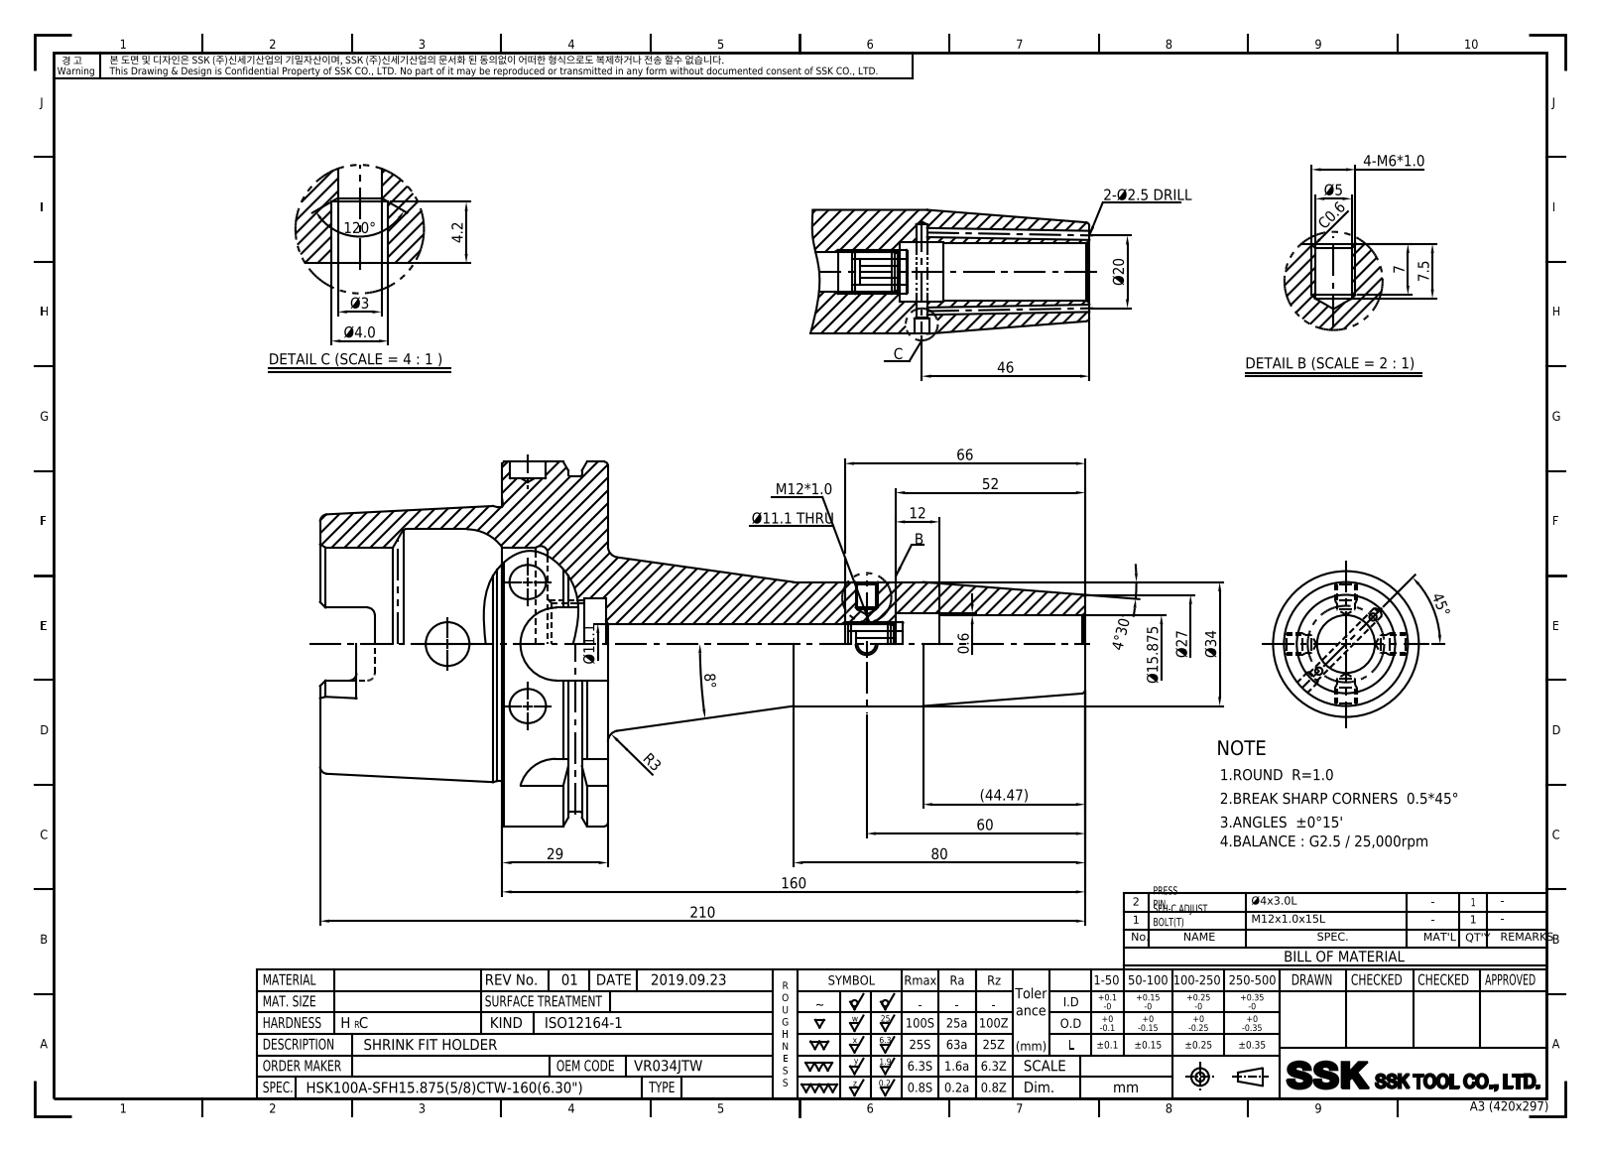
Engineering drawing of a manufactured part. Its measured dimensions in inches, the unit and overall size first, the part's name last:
Units: inches
Overall size (bounding box): 8.268 × 3.937 × 3.937
Round holes (diameter × count): ⌀0.079 ×2, ⌀0.394 ×1, ⌀0.43 ×1, ⌀0.472 ×1, ⌀0.625 ×1, ⌀0.672 ×1, ⌀0.881 ×1, ⌀0.984 ×1, ⌀2.087 ×1, ⌀2.48 ×1
Round bosses / shafts (diameter × count): ⌀3.937 ×1, ⌀3.622 ×1, ⌀2.969 ×1, ⌀1.339 ×1
Partial cylindrical surfaces — rounded edges, fillets, slot ends (radius × count): R0.079 ×6, R0.192 ×4, R0.394 ×4
Main face-to-face distances: 1.142, 0.492, 0.65, 3.11, 2.461, 1.969, 3.465, 3.091, 1.122, 0.63
Volume: 22.54 in³ · Surface area: 107.1 in²
Bodies: 1 solid, 118 faces (38 planar, 36 cylindrical, 44 other)
Part name (STEP PRODUCT): LO-HSK100A-SFH15.875CTW-160
STEP written by: Autodesk Inventor 2022 (AUTOMOTIVE_DESIGN)
